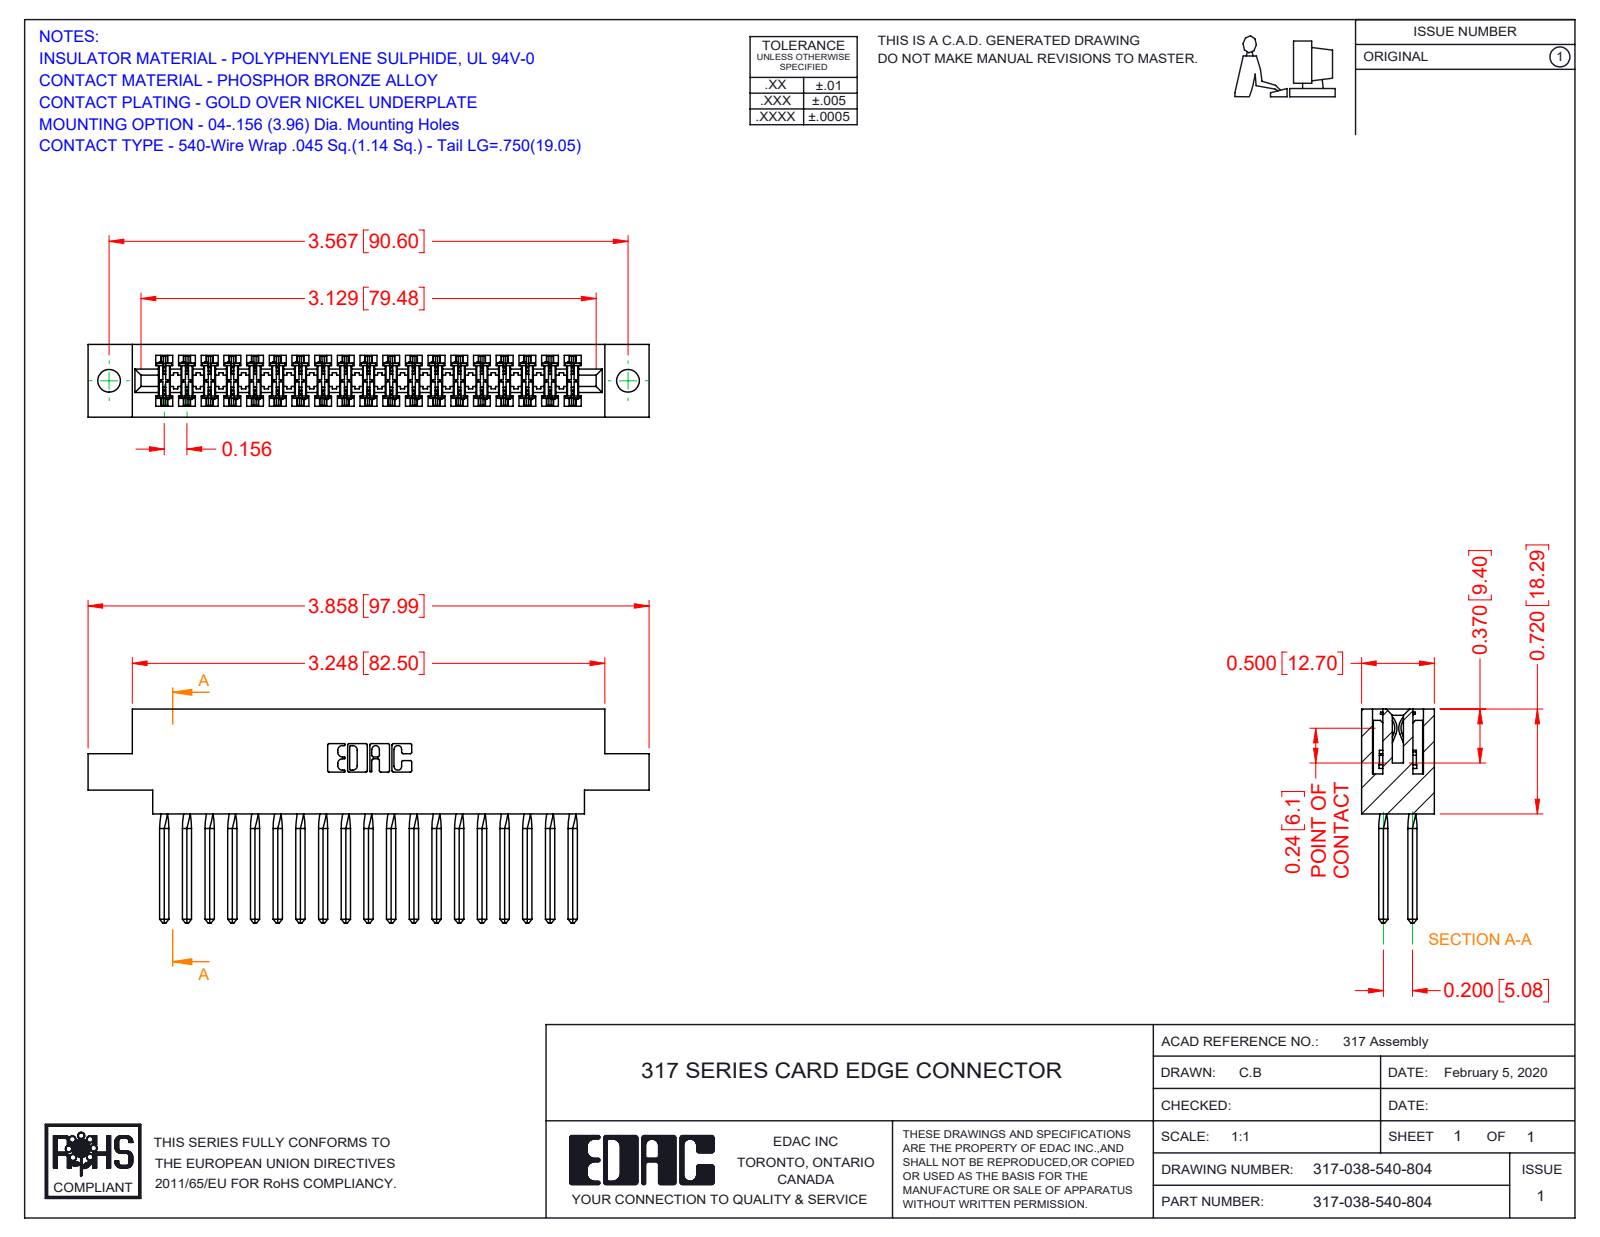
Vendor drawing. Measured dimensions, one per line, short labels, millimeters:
name: 317 Part_.156 Dia - TH; 317-290-001_540; 317-038-540-804
written by: SolidWorks 2016 (CONFIG_CONTROL_DESIGN)
unit: mm
bodies: 39 solids, 3484 faces (2832 planar, 500 cylindrical, 152 other)
size: 98 × 37.3 × 12.7
volume: 15 600 mm³; area: 22 190 mm²
holes: 2× ⌀4
rounds: 76× R0.4, 22× R0.3, 6× R0.2, 6× R0.8, 3× R0.7, 2× R2.4, 2× R2.5, 2× R2.8
face distances: 12.7, 1.9, 10.8, 2.8, 8.9, 5, 5.6, 18.3, 2.4, 5.1
hole spacings: 90.6
